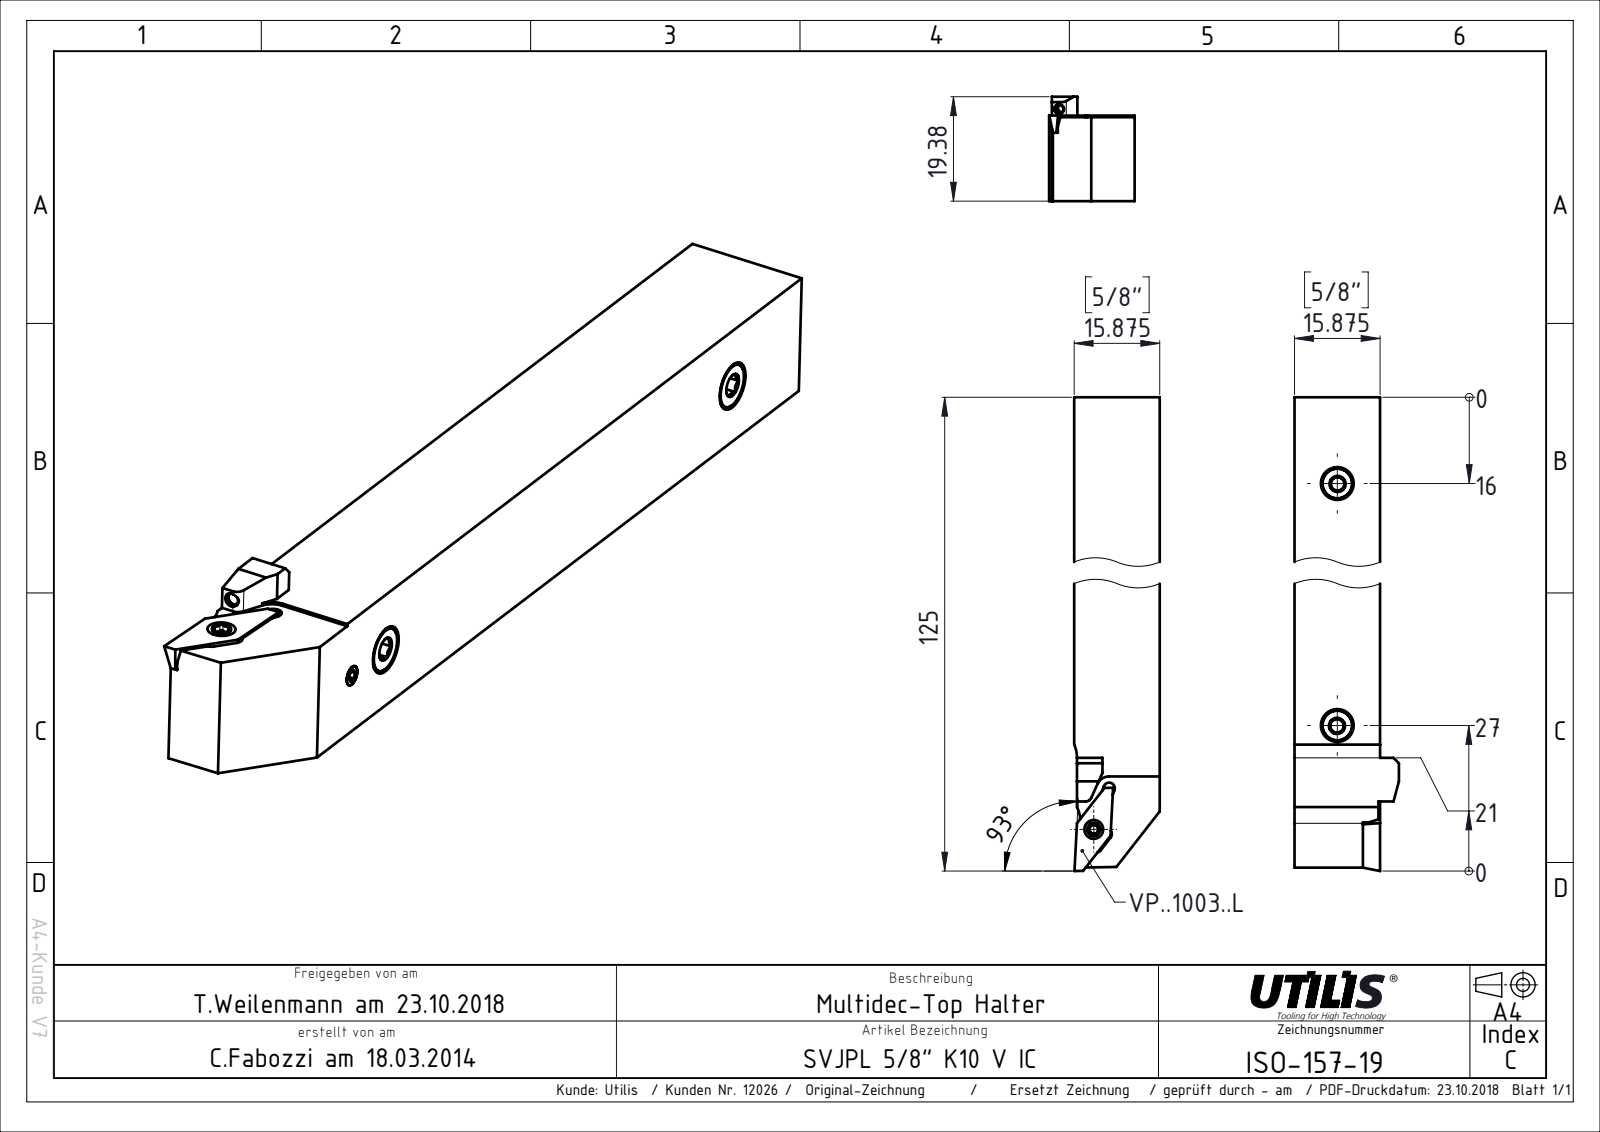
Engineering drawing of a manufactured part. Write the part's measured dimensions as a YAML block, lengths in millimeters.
part_name: "ISO-157-19"
step_written_by: "SolidWorks 2015 (AUTOMOTIVE_DESIGN)"
units: millimeters
bodies: {solids: 1, faces: 70, planar: 57, cylindrical: 9, other: 4}
overall_size: [128.3, 19.38, 16.07]
volume: 30970
surface_area: 8607
round_bosses_or_shafts:
  - {diameter: 14, count: 1}
partial_cylinders:
  - {radius: 1.05, count: 3}
  - {radius: 6.1, count: 2}
  - {radius: 2.3, count: 1}
face_to_face_distances: [15.88, 15.61, 15.58, 3.3, 5, 19.38, 3.8, 3.5, 12.7, 2.88]
